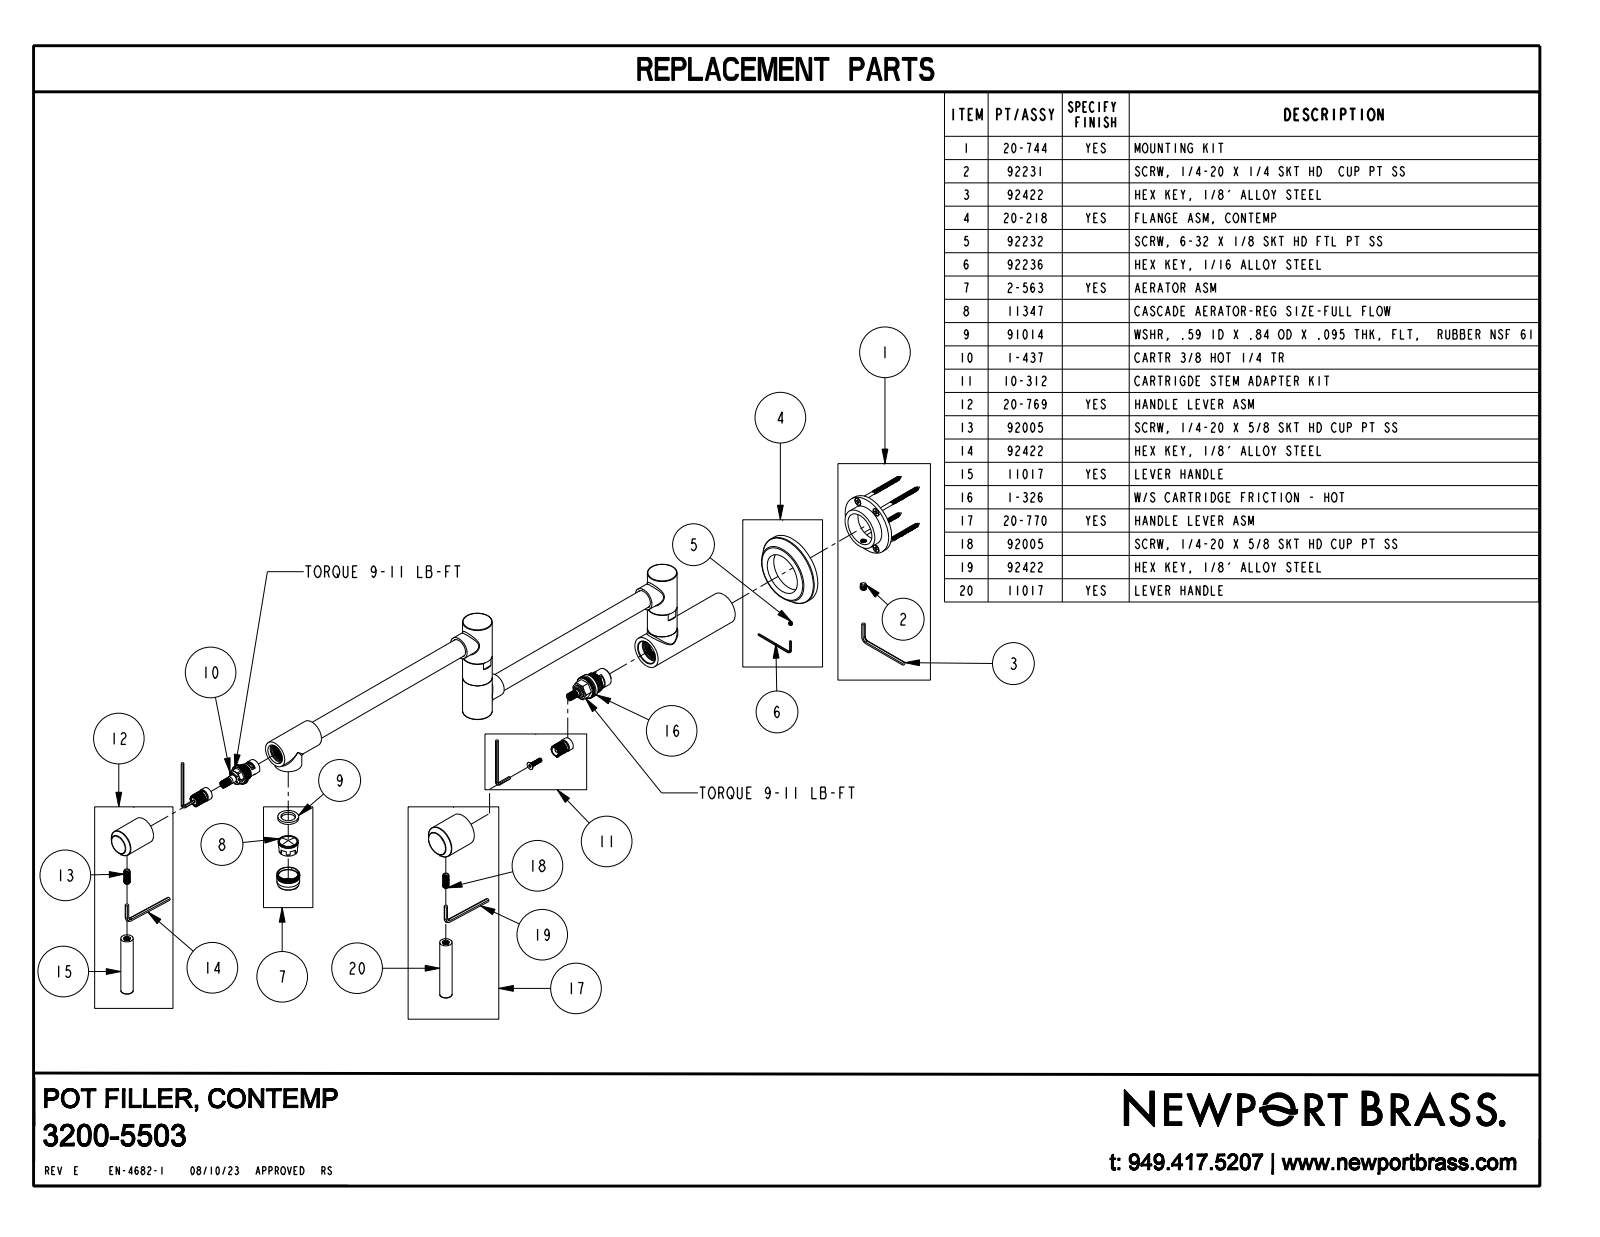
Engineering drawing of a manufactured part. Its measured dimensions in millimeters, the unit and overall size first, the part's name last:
Units: millimetres
Overall size (bounding box): 689 × 239.2 × 74.2
Round bosses / shafts (diameter × count): ⌀23.9 ×4, ⌀30.5 ×2, ⌀27.9 ×2, ⌀19.1 ×2, ⌀12.7 ×2, ⌀74.2 ×1, ⌀33.7 ×1, ⌀23.5 ×1
Partial cylindrical surfaces — rounded edges, fillets, slot ends (radius × count): R12 ×1
Main face-to-face distances: 14.5, 72.6, 40, 112.7, 42.6, 0.5, 43.1, 112.8, 98.3, 150
Volume: 531 400 mm³ · Surface area: 89 940 mm²
Bodies: 1 solid, 129 faces (32 planar, 44 cylindrical, 53 other)
Part name (STEP PRODUCT): 3200-5503
STEP written by: CREO PARAMETRIC BY PTC INC, 2018400 (CONFIG_CONTROL_DESIGN)
